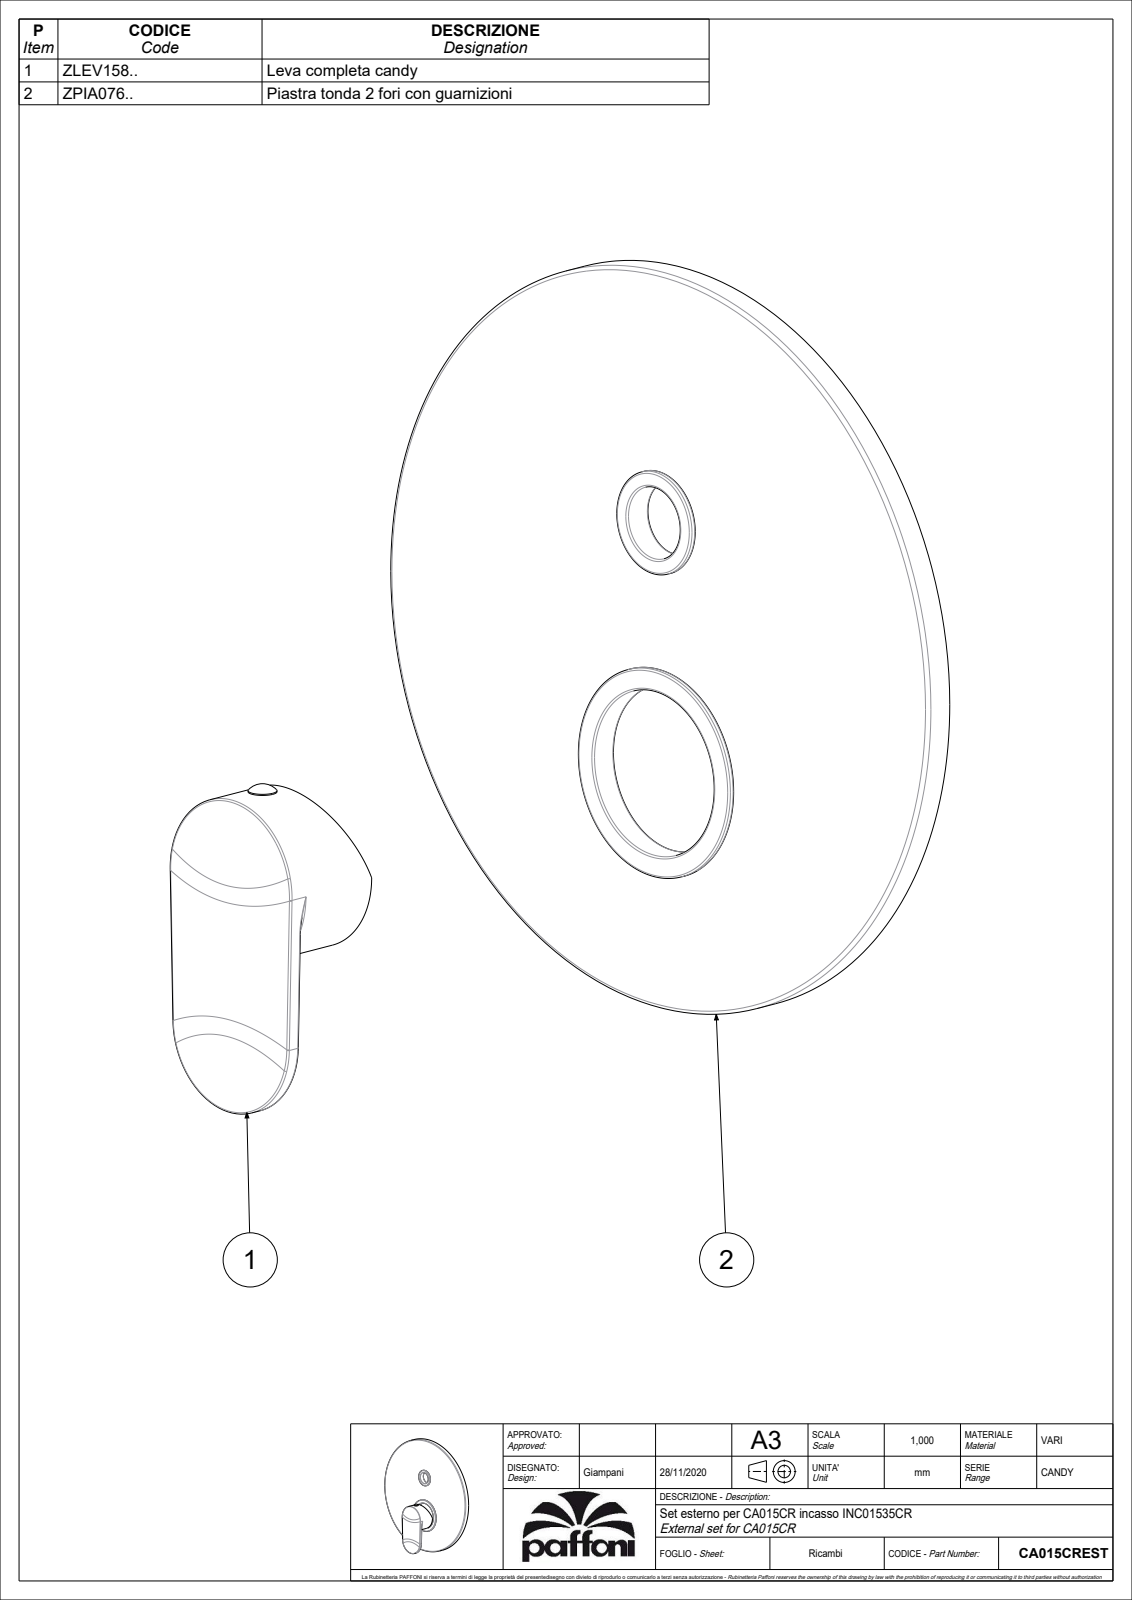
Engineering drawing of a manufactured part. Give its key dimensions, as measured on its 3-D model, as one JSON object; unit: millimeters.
{"part_name": "CA015CREST", "step_written_by": "CREO PARAMETRIC BY PTC INC, 2020044 (CONFIG_CONTROL_DESIGN)", "units": "millimeters", "bodies": {"solids": 2, "faces": 186, "planar": 55, "cylindrical": 53, "other": 78}, "overall_size": [200, 200, 44], "volume_mm3": 167605, "surface_area_mm2": 95194, "round_holes": [[3, 1], [19.1, 1], [44.6, 1], [50, 1], [145, 1], [198, 1]], "round_bosses_or_shafts": [[200, 1], [195, 1], [56.2, 1], [49.9, 1], [45, 1], [25.1, 1], [23.5, 1], [7.6, 1]], "partial_cylinders_radius": [[1, 4], [3, 4], [3.5, 1], [21.5, 1]], "face_to_face_distances": [1, 8, 9, 33, 32, 41, 2, 3, 30, 11], "hole_center_spacings": [32.2, 35.8, 68]}
